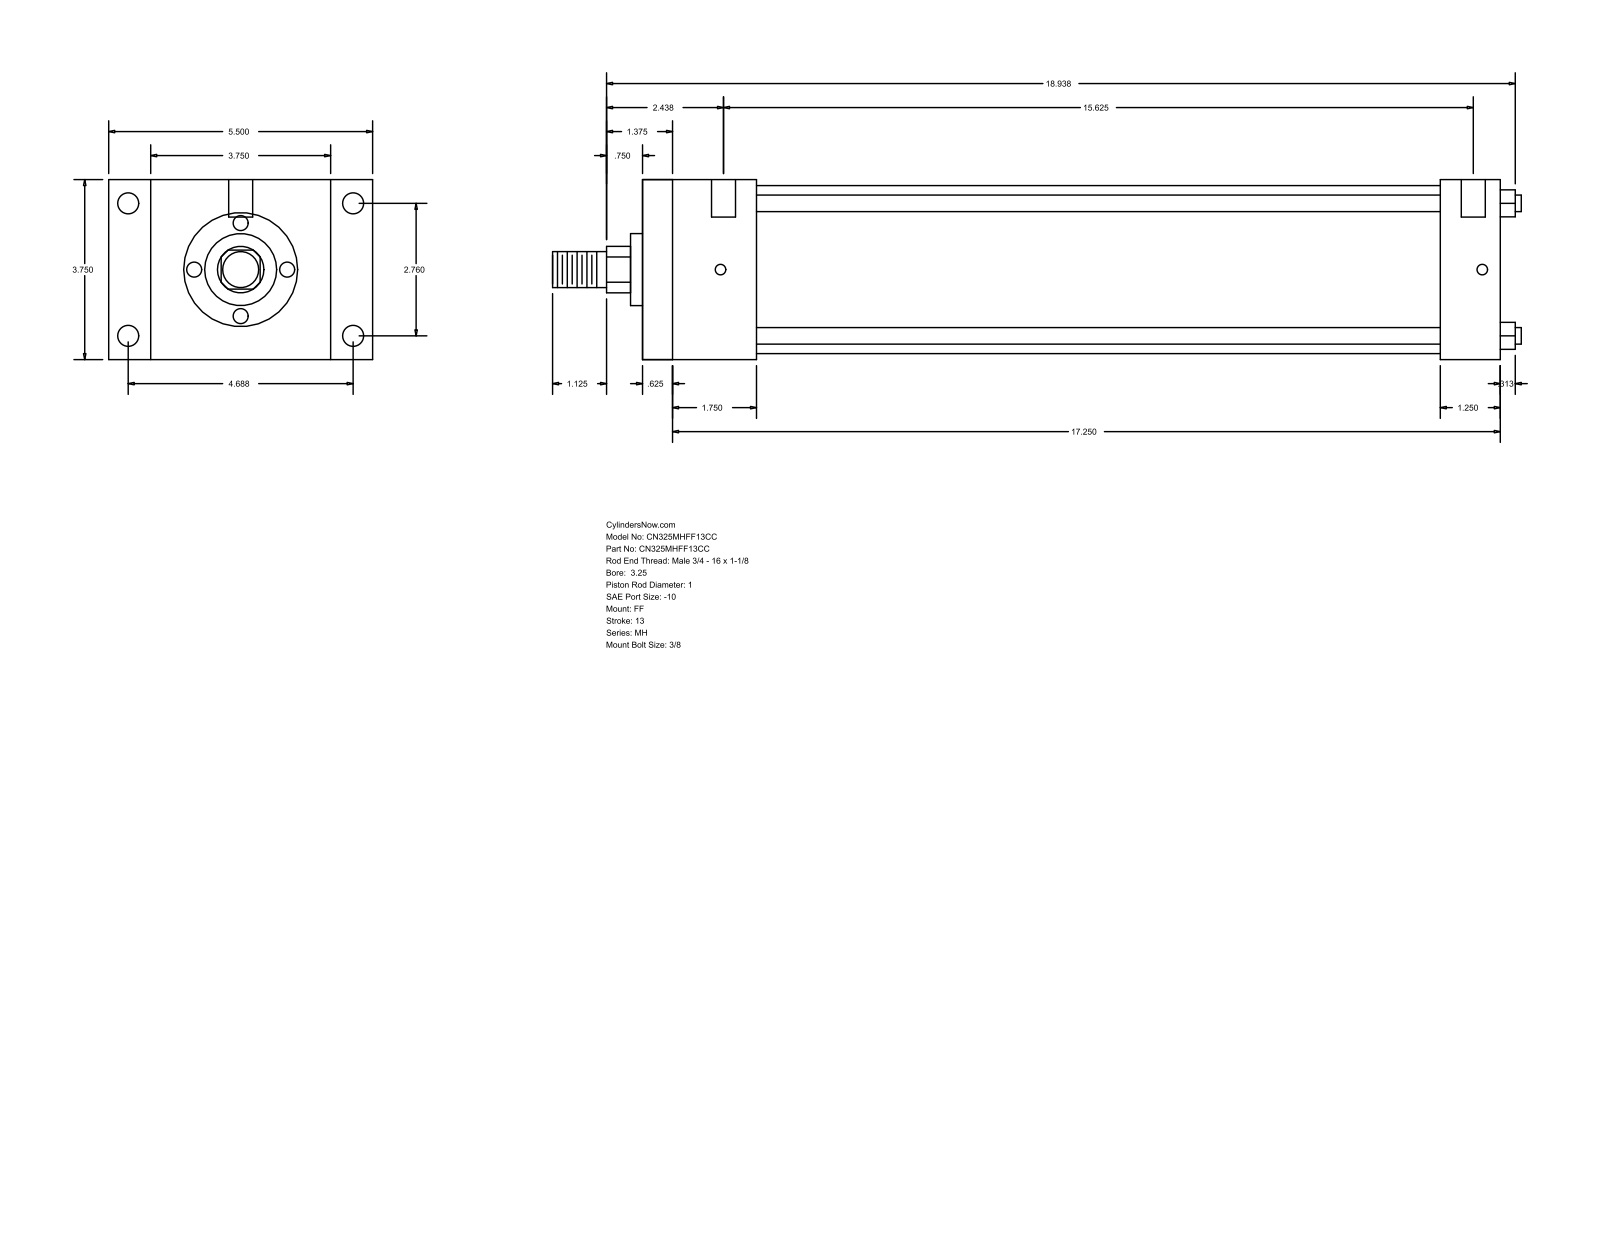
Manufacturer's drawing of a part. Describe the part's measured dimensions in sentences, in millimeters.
The part is named "MH_FF__0325_1". Its 3-D file was written by "GSSL Pune (CONFIG_CONTROL_DESIGN)". It is 0 solids with 92 faces: 64 planar, 28 cylindrical and 0 other. Overall it measures 512.76 by 139.7 by 95.25 millimeters. Round holes: 4 of diameter 5.56, 4 of diameter 11.13, 2 of diameter 12.7. Round bosses or shafts: 4 of diameter 8.76, 1 of diameter 88.9, 1 of diameter 38.1, 1 of diameter 25.4, 1 of diameter 19.05. Partial cylindrical surfaces (rounded edges, fillets, slot ends): 1 of radius 12.29. The main face-to-face distances are 95.24, 454.02, 15.87, 438.15, 22.23, 117.47, 422.27, 406.4, 31.75, 60.33. The hole center spacings are 70.1, 119.06, 138.16, 403.22, 1.58, 4.76, 396.88, 398.46.
